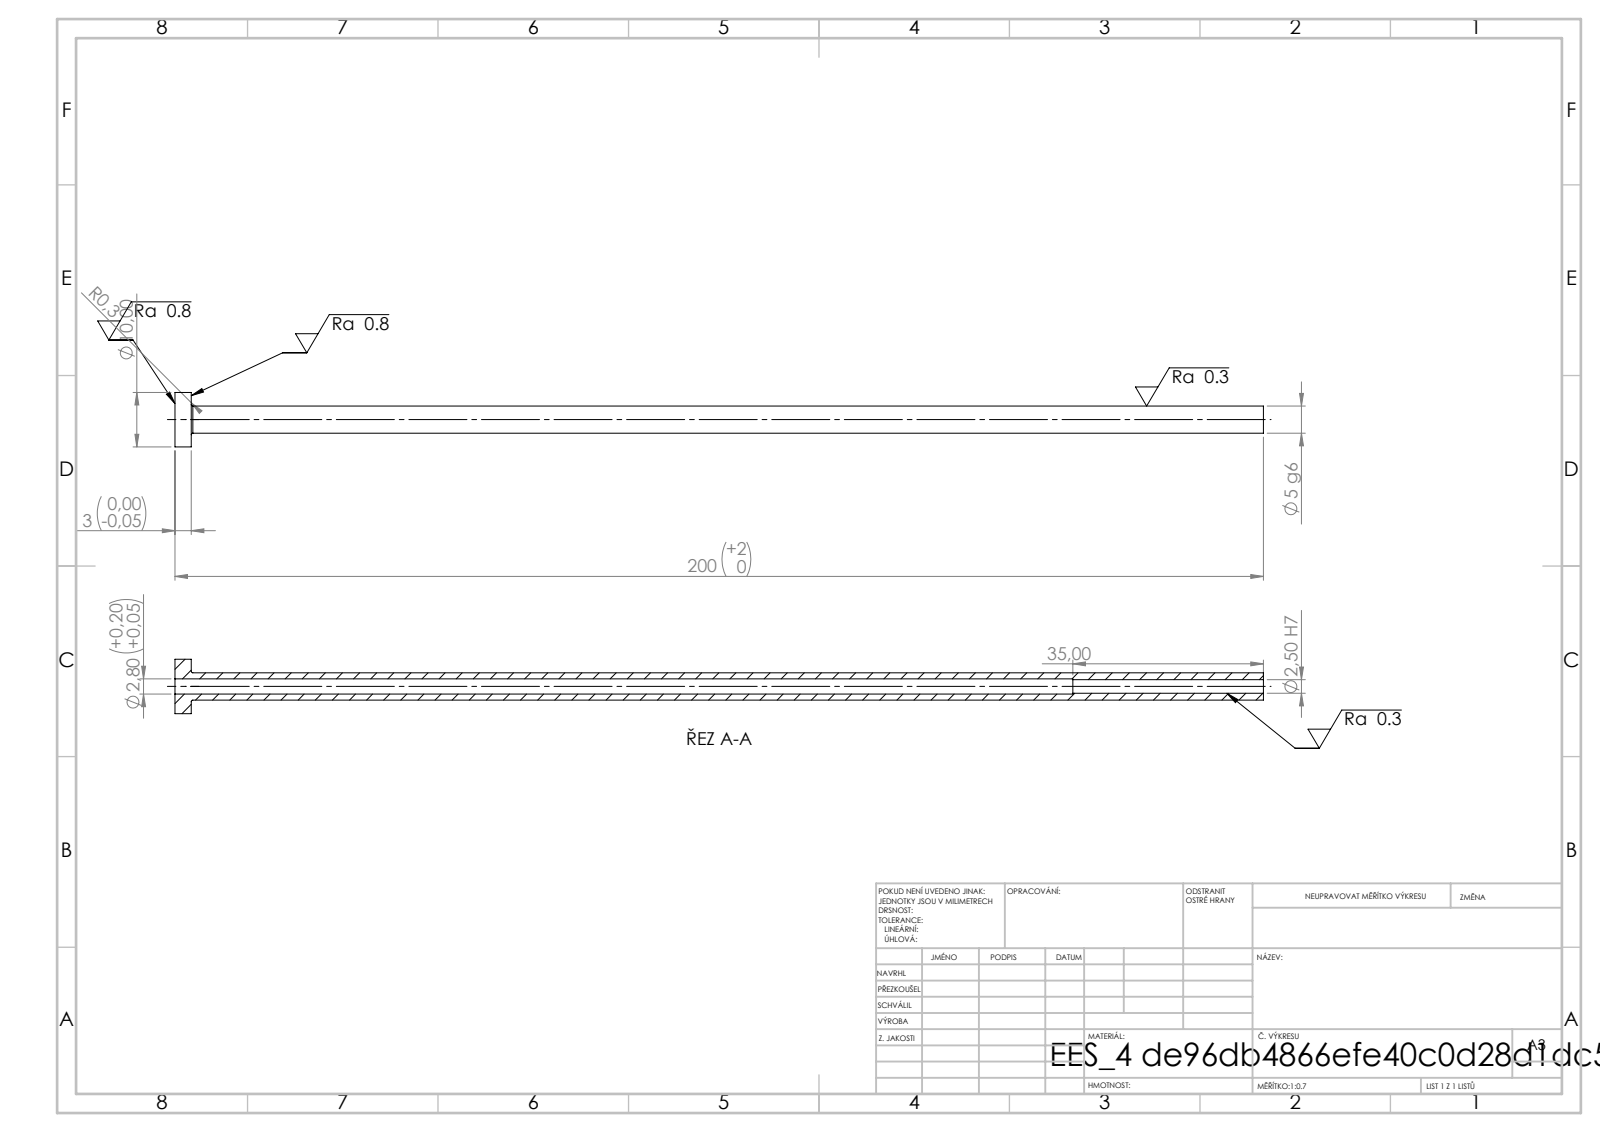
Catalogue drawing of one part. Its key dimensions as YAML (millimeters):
step_written_by: "SolidWorks 2019 (CONFIG_CONTROL_DESIGN)"
units: millimeters
bodies: {solids: 1, faces: 14, planar: 4, cylindrical: 8, other: 2}
overall_size: [200, 10, 10]
volume: 2916
surface_area: 5060
round_holes:
  - {diameter: 2.5, count: 1}
  - {diameter: 2.8, count: 1}
round_bosses_or_shafts:
  - {diameter: 10, count: 1}
  - {diameter: 5, count: 1}
face_to_face_distances: [3, 200, 197, 165, 162, 35]
